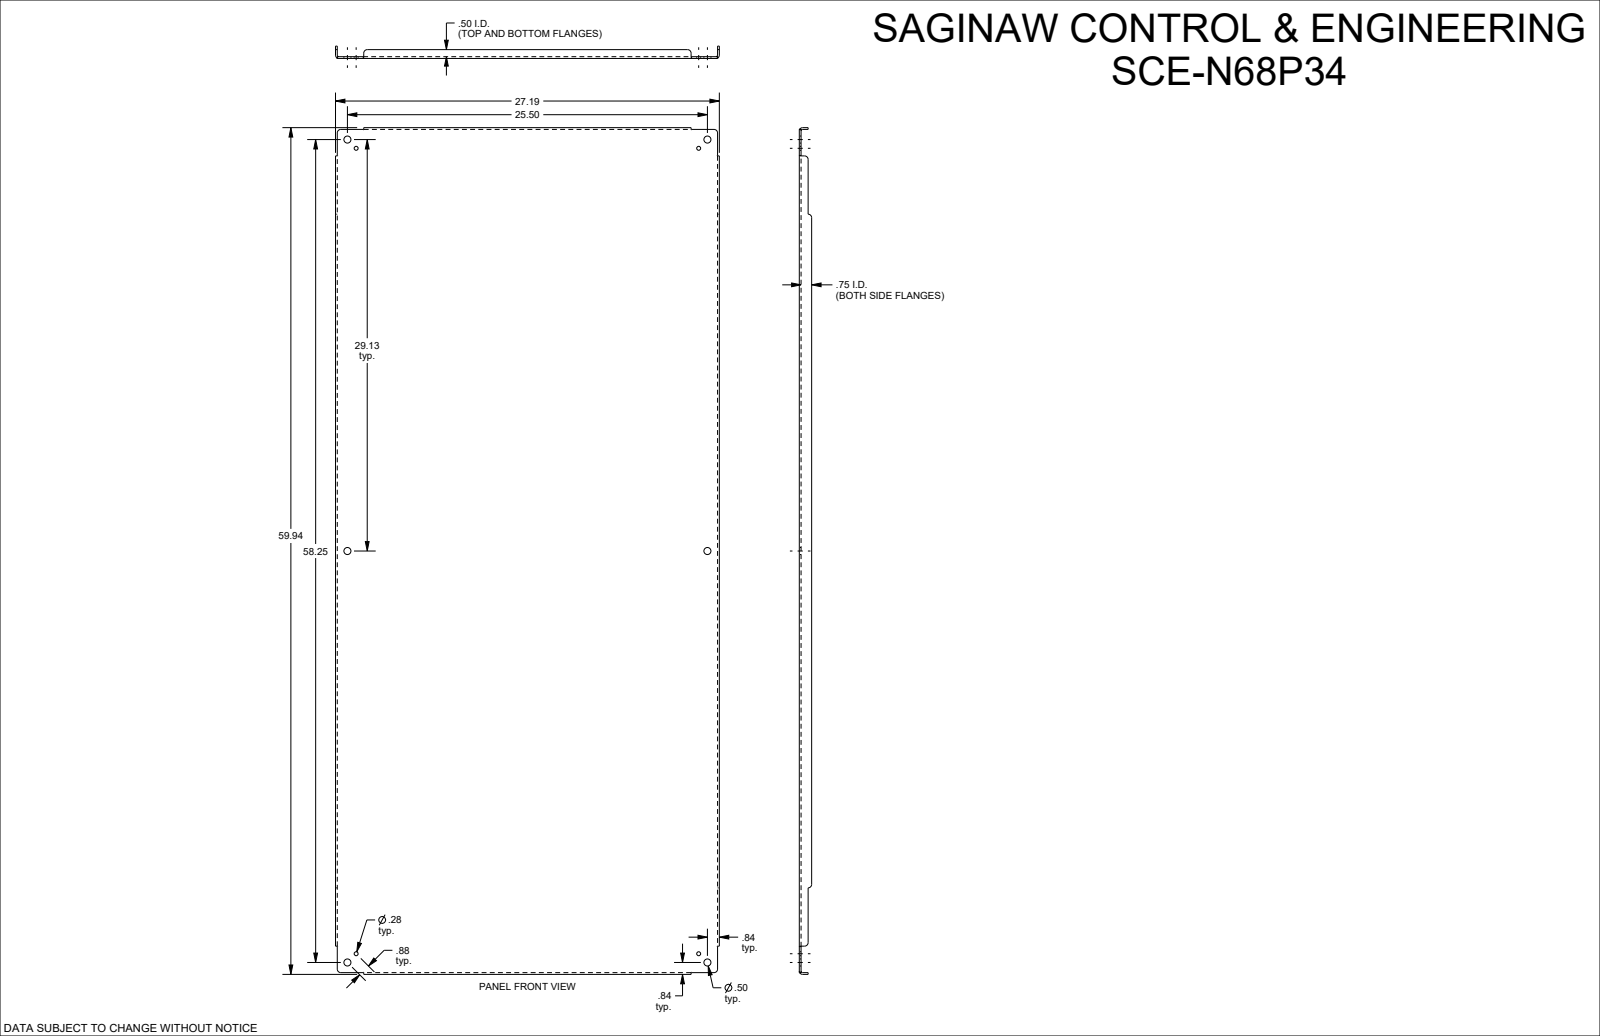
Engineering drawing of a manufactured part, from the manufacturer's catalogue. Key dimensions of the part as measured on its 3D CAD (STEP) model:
Part name (STEP PRODUCT): SCE-N68P34
STEP written by: SolidWorks 2023 (AUTOMOTIVE_DESIGN)
Units: inches
Bodies: 1 solid, 110 faces (42 planar, 44 cylindrical, 24 other)
Overall size (bounding box): 59.938 × 27.188 × 0.875
Volume: 214.6 in³ · Surface area: 3 458 in²
Round holes (diameter × count): ⌀0.5 ×6, ⌀0.281 ×4
Partial cylindrical surfaces — rounded edges, fillets, slot ends (radius × count): R0.25 ×10, R0.112 ×4, R0.237 ×4
Main face-to-face distances: 0.125, 27.063, 26.938, 27.187, 0.125, 59.813, 0.75, 0.875, 59.687, 59.938
Hole centre spacings: 0.875, 24.889, 28.513, 29.125, 37.837, 38.711, 57.634, 62.773
